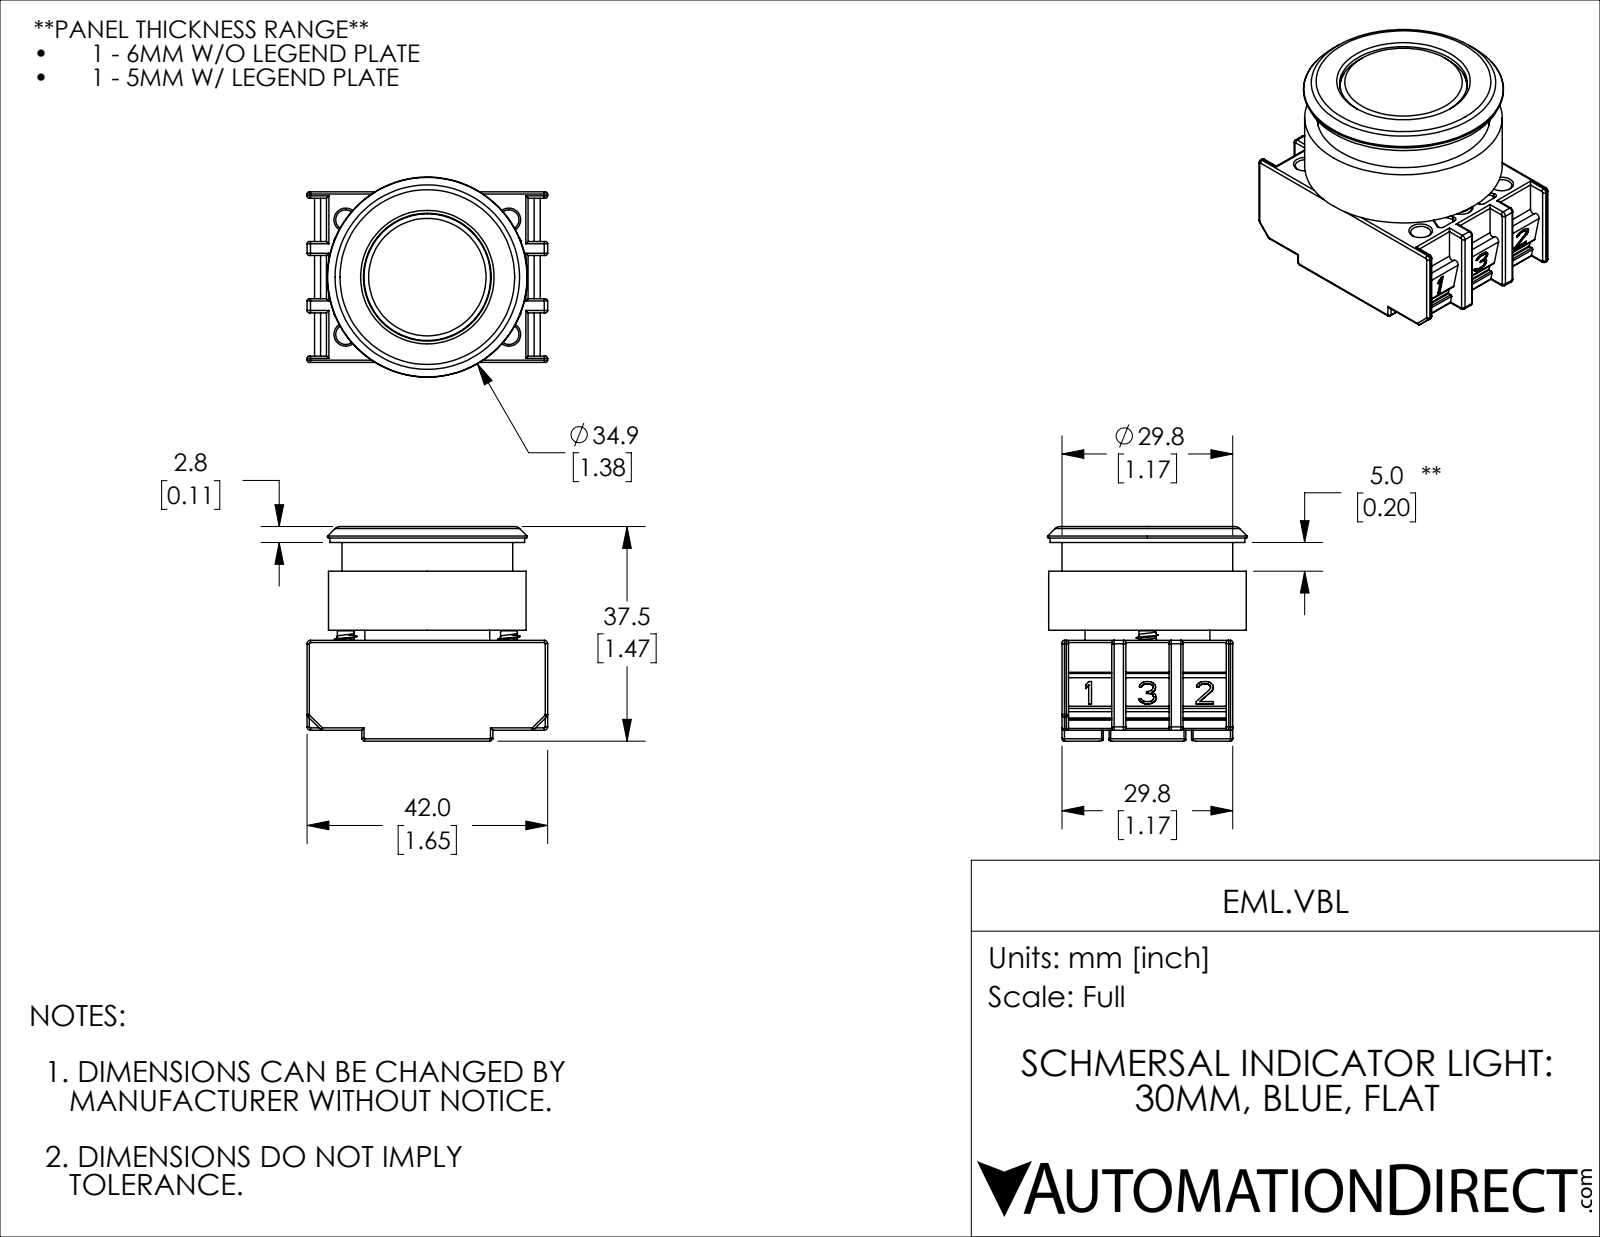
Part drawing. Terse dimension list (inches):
name: EML.VBL
written by: SolidWorks 2019 (CONFIG_CONTROL_DESIGN)
unit: in
bodies: 3 solids, 1372 faces (495 planar, 474 cylindrical, 403 other)
size: 1.654 × 1.474 × 1.375
volume: 1.358 in³; area: 33.49 in²
holes: 6× ⌀0.138, 6× ⌀0.203, 1× ⌀0.433, 1× ⌀0.496, 1× ⌀0.591, 1× ⌀0.709, 1× ⌀0.878, 1× ⌀0.953, 1× ⌀1.024, 1× ⌀1.063, 1× ⌀1.189
bosses: 2× ⌀0.189, 2× ⌀0.115, 1× ⌀1.358, 1× ⌀1.339, 1× ⌀1.173, 1× ⌀1.004, 1× ⌀0.945, 1× ⌀0.937
rounds: 115× R0.016, 48× R0.012, 28× R0.008, 8× R0.024, 6× R0.02, 2× R0.004, 2× R0.024, 2× R0.031
face distances: 1.173, 0.579, 0.069, 0.648, 0.134, 0.394, 0.075, 0.762, 0.774, 0.705
hole spacings: 0.394, 0.685, 1.189, 1.122, 0.561, 0.787, 1.371
